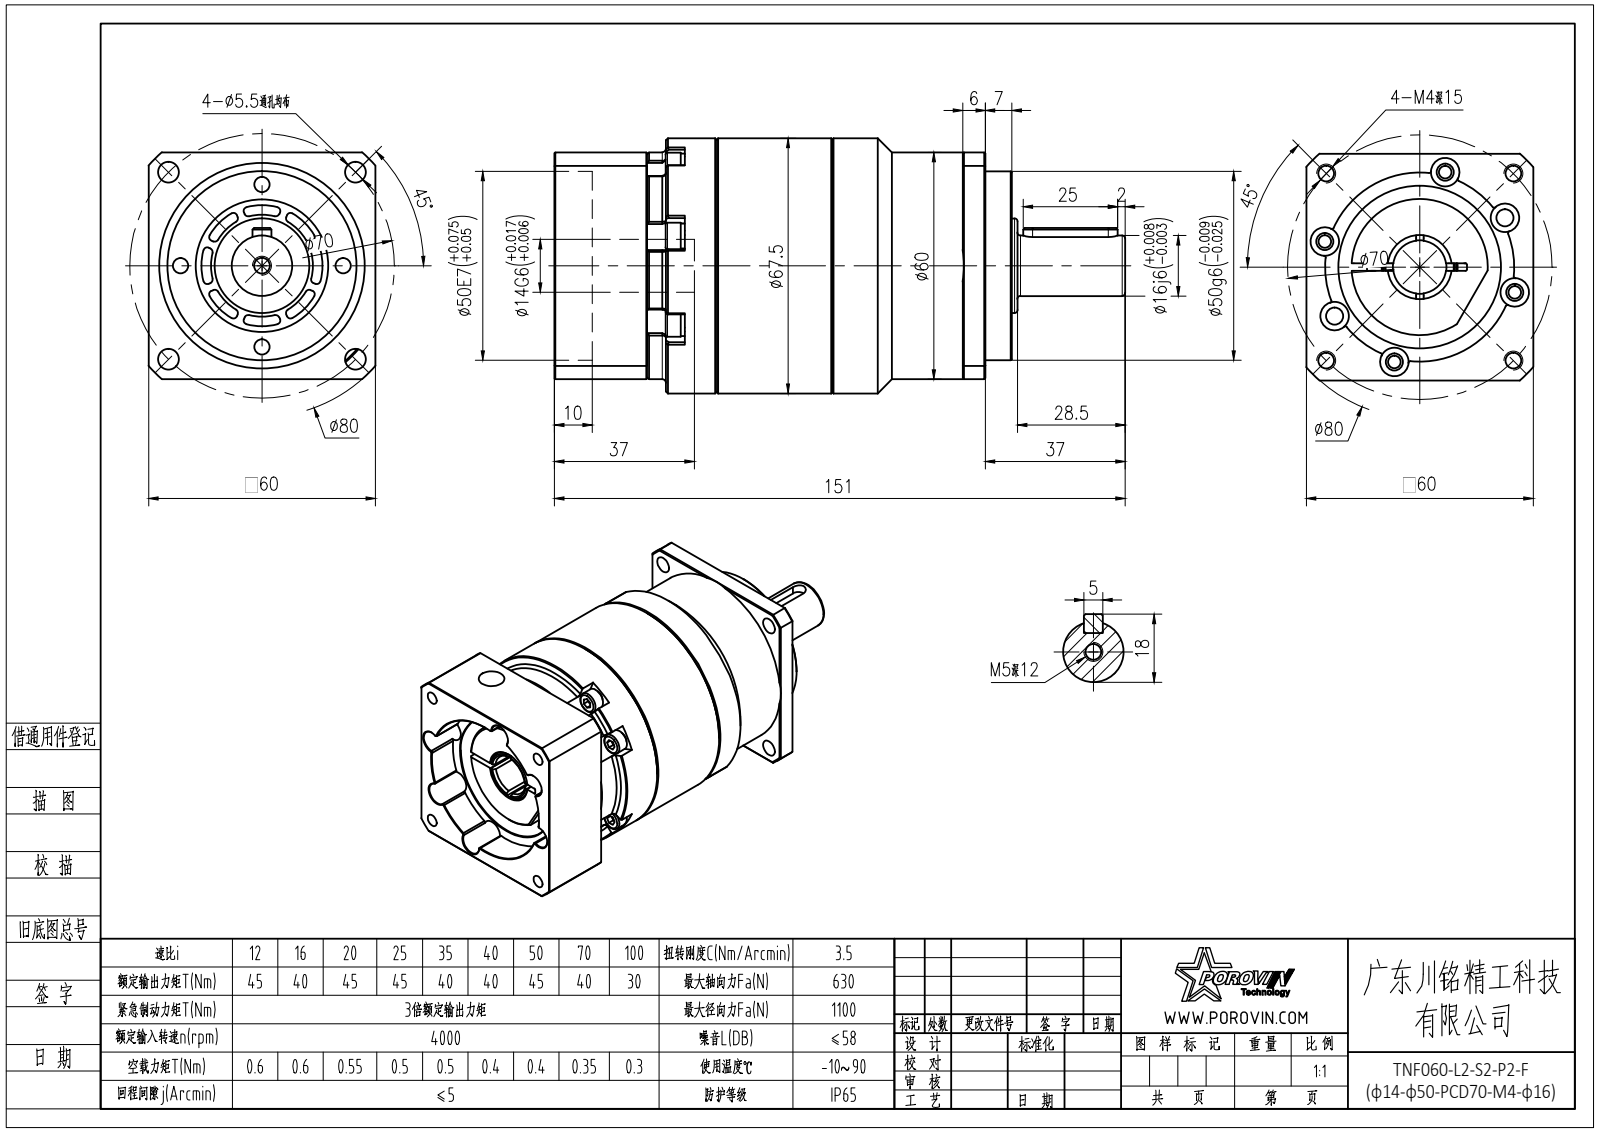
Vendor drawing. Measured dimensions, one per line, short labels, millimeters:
name: hexagon socket head cap screws gb_GB_FASTENER_SCREWS_HSHCS M4X20-N; hexagon socket head cap screws gb_GB_FASTENER_SCREWS_HSHCS M5X16-N; 二级齿圈 KS60外形图; hex socket set screws with flat point gb_GB_FASTENER_SCREWS_HSFP M10X10-N (+3 more)
written by: SolidWorks 2016 (CONFIG_CONTROL_DESIGN)
unit: mm
bodies: 33 solids, 1089 faces (409 planar, 400 cylindrical, 280 other)
size: 151 × 67.5 × 67.5
volume: 284 472 mm³; area: 81 571 mm²
holes: 12× ⌀4.4, 12× ⌀4.5, 10× ⌀3.3, 6× ⌀7.5, 5× ⌀5.5, 4× ⌀4, 2× ⌀4.2, 1× ⌀5.2, 1× ⌀8.5, 1× ⌀14, 1× ⌀14.2, 1× ⌀25
bosses: 12× ⌀7, 12× ⌀6.6, 12× ⌀4, 1× ⌀67.5, 1× ⌀60, 1× ⌀36, 1× ⌀22.5, 1× ⌀20
rounds: 36× R0.5, 32× R1, 6× R3.75, 2× R2.5, 1× R4.75, 1× R13.5, 1× R16, 1× R40
face distances: 29, 60, 67, 22.5, 51.5, 5, 38, 89.5, 34, 33
hole spacings: 24.96, 52.46, 8.62, 26, 30.5, 7.64, 16.02, 18.02
